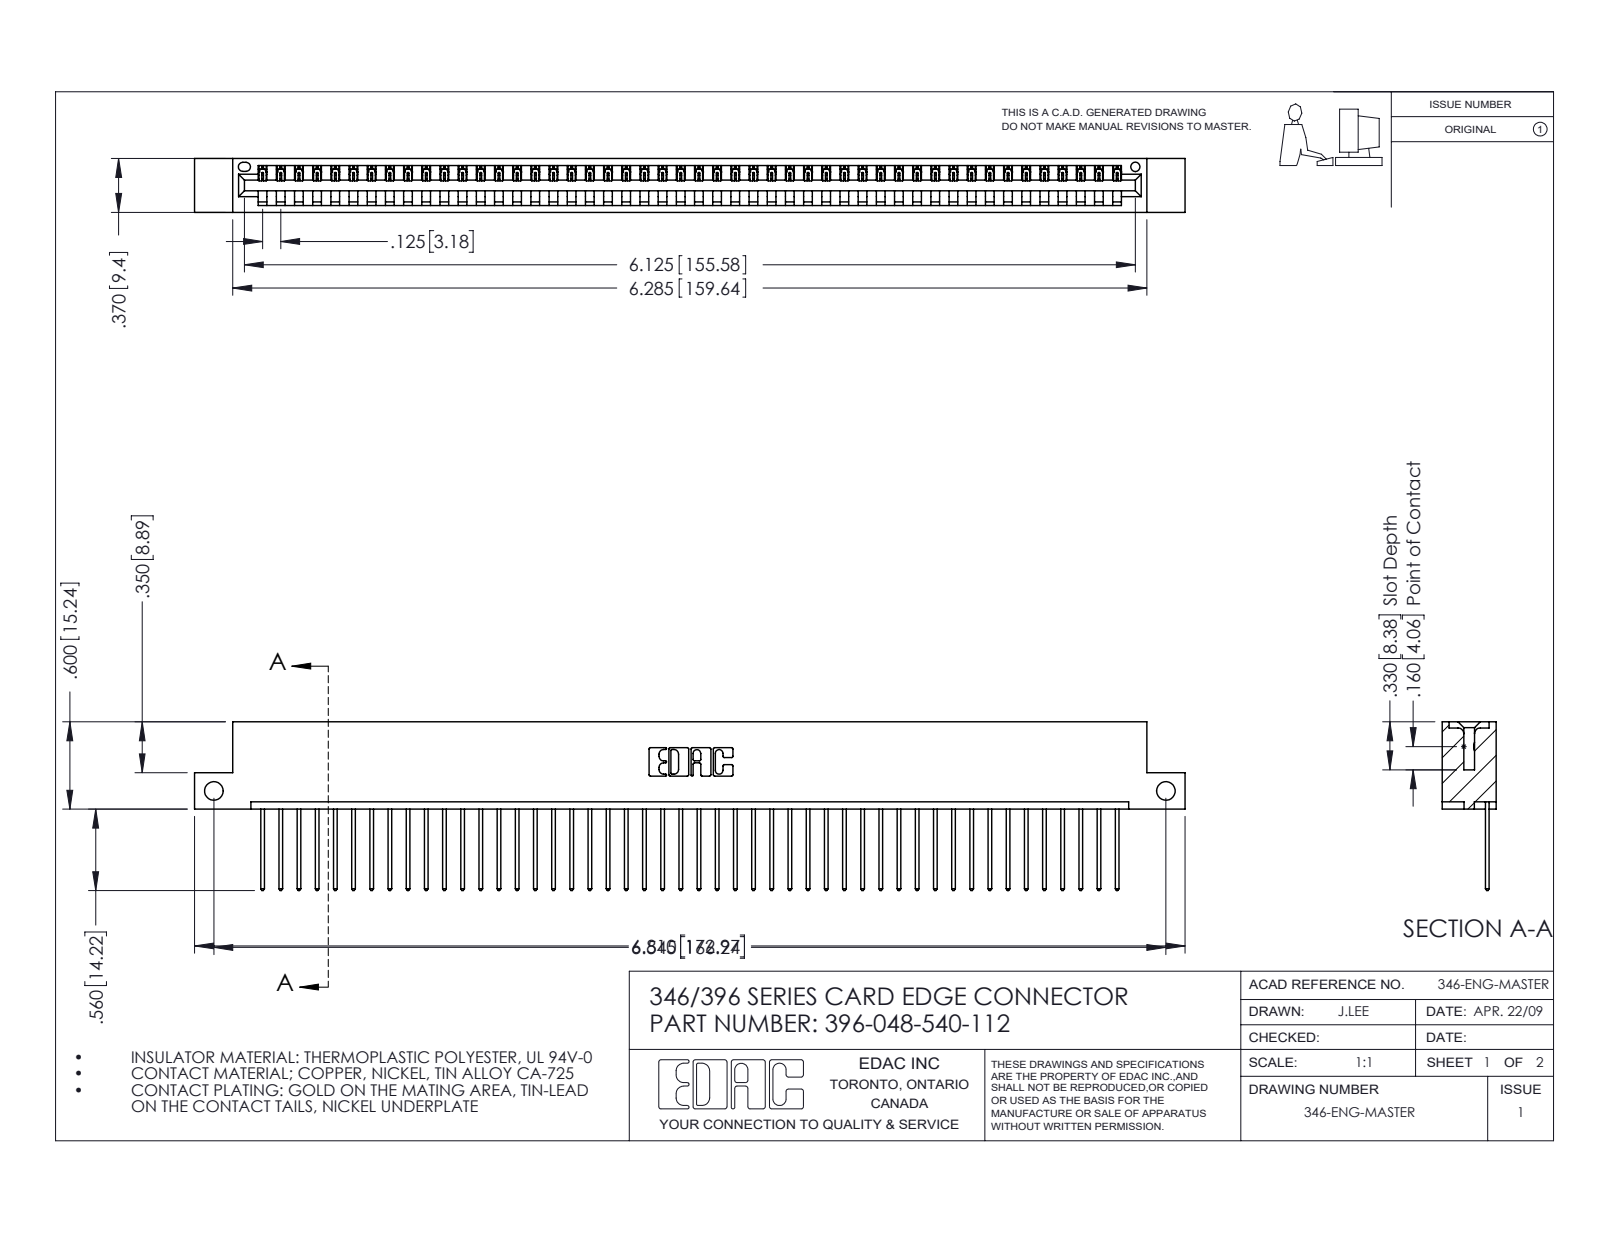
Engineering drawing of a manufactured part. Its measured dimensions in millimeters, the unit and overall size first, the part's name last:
Units: millimetres
Overall size (bounding box): 173 × 29.5 × 9.4
Round holes (diameter × count): ⌀3.3 ×2, ⌀1.6 ×1
Partial cylindrical surfaces — rounded edges, fillets, slot ends (radius × count): R0.2 ×96, R0.3 ×96, R0.3 ×22, R0.2 ×6, R0.8 ×6, R0.7 ×3, R0.8 ×2, R1 ×2
Main face-to-face distances: 1.2, 8.2, 9.4, 6.4, 1.8, 7.6, 0.6, 3.8, 5.6, 2.5
Hole centre spacings: 166.2
Volume: 16 580 mm³ · Surface area: 21 110 mm²
Bodies: 49 solids, 2906 faces (1996 planar, 910 cylindrical, 0 other)
Part name (STEP PRODUCT): 346 Part_Flush Mounting Lugs - Side Mount; 396-048-540-112; 345-292-001_345-293-140
STEP written by: SolidWorks 2016 (CONFIG_CONTROL_DESIGN)
